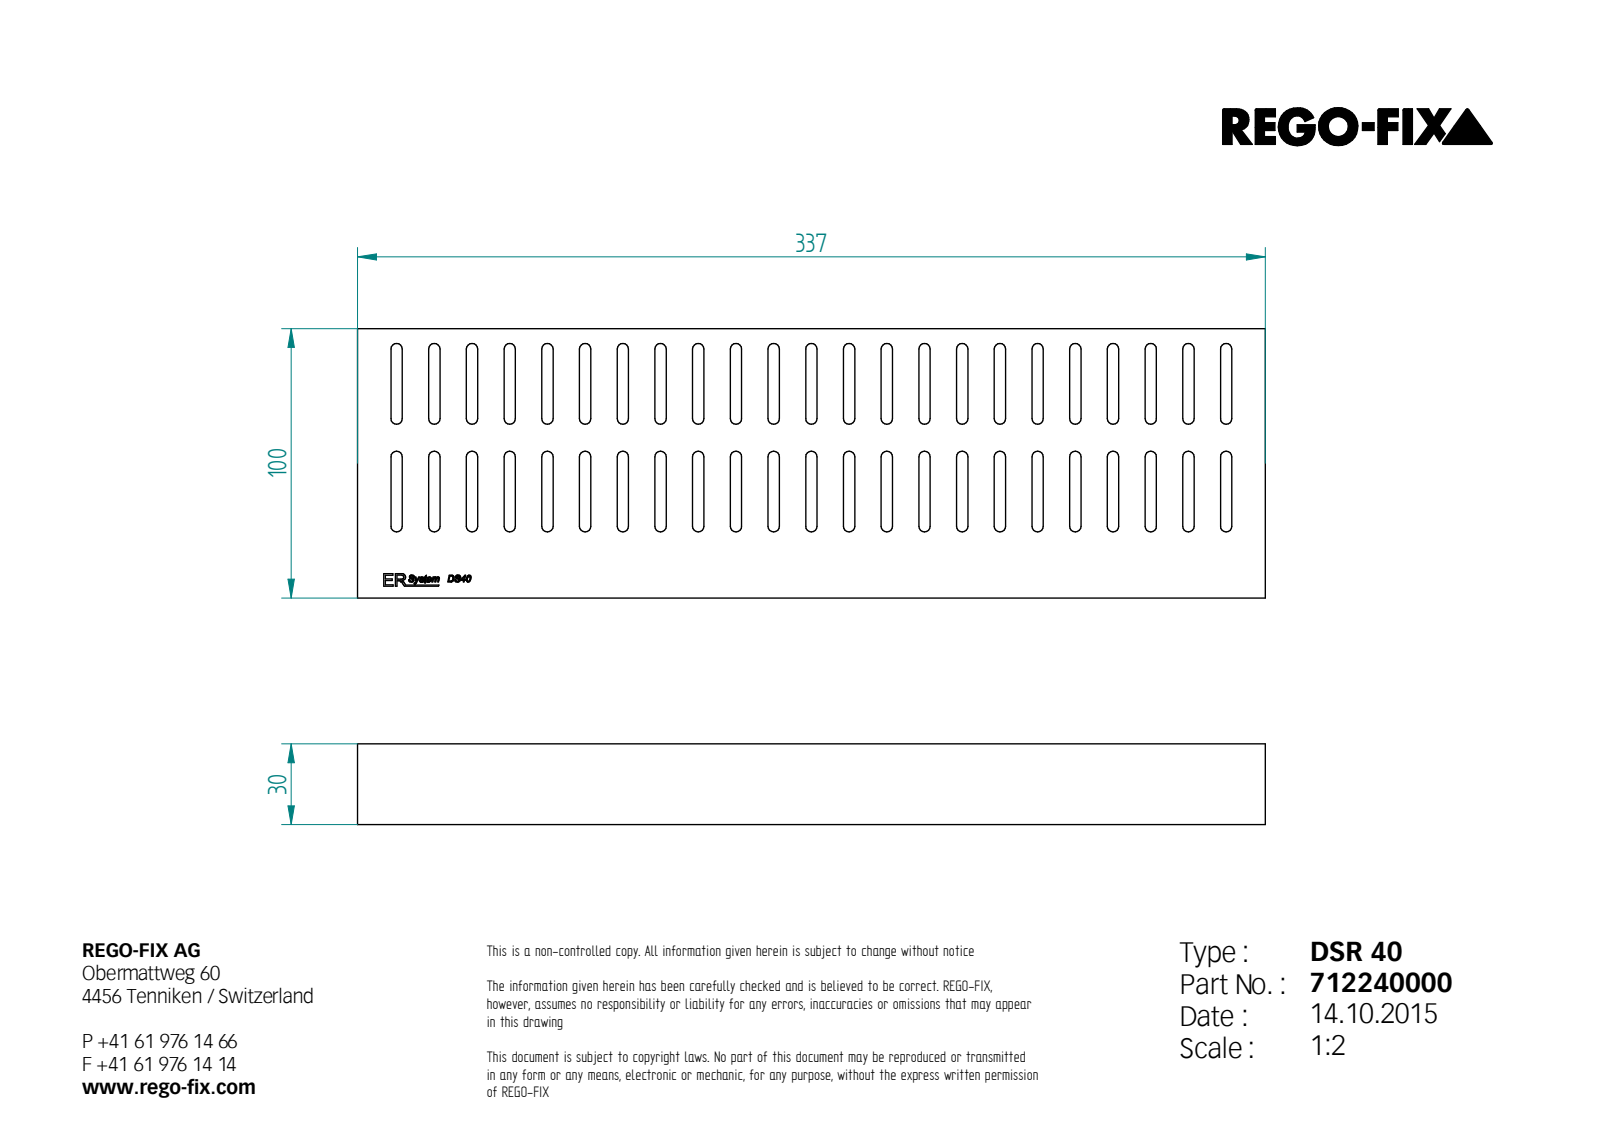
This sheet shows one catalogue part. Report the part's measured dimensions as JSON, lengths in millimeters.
{"step_written_by": "Unknown (AUTOMOTIVE_DESIGN)", "units": "millimeters", "bodies": {"solids": 1, "faces": 344, "planar": 226, "cylindrical": 92, "other": 26}, "overall_size": [337, 100, 30], "volume_mm3": 960400, "surface_area_mm2": 120484, "partial_cylinders_radius": [[2.1, 92]], "face_to_face_distances": [30, 100, 14, 28, 21, 9, 42, 56, 4.2, 18.2]}
